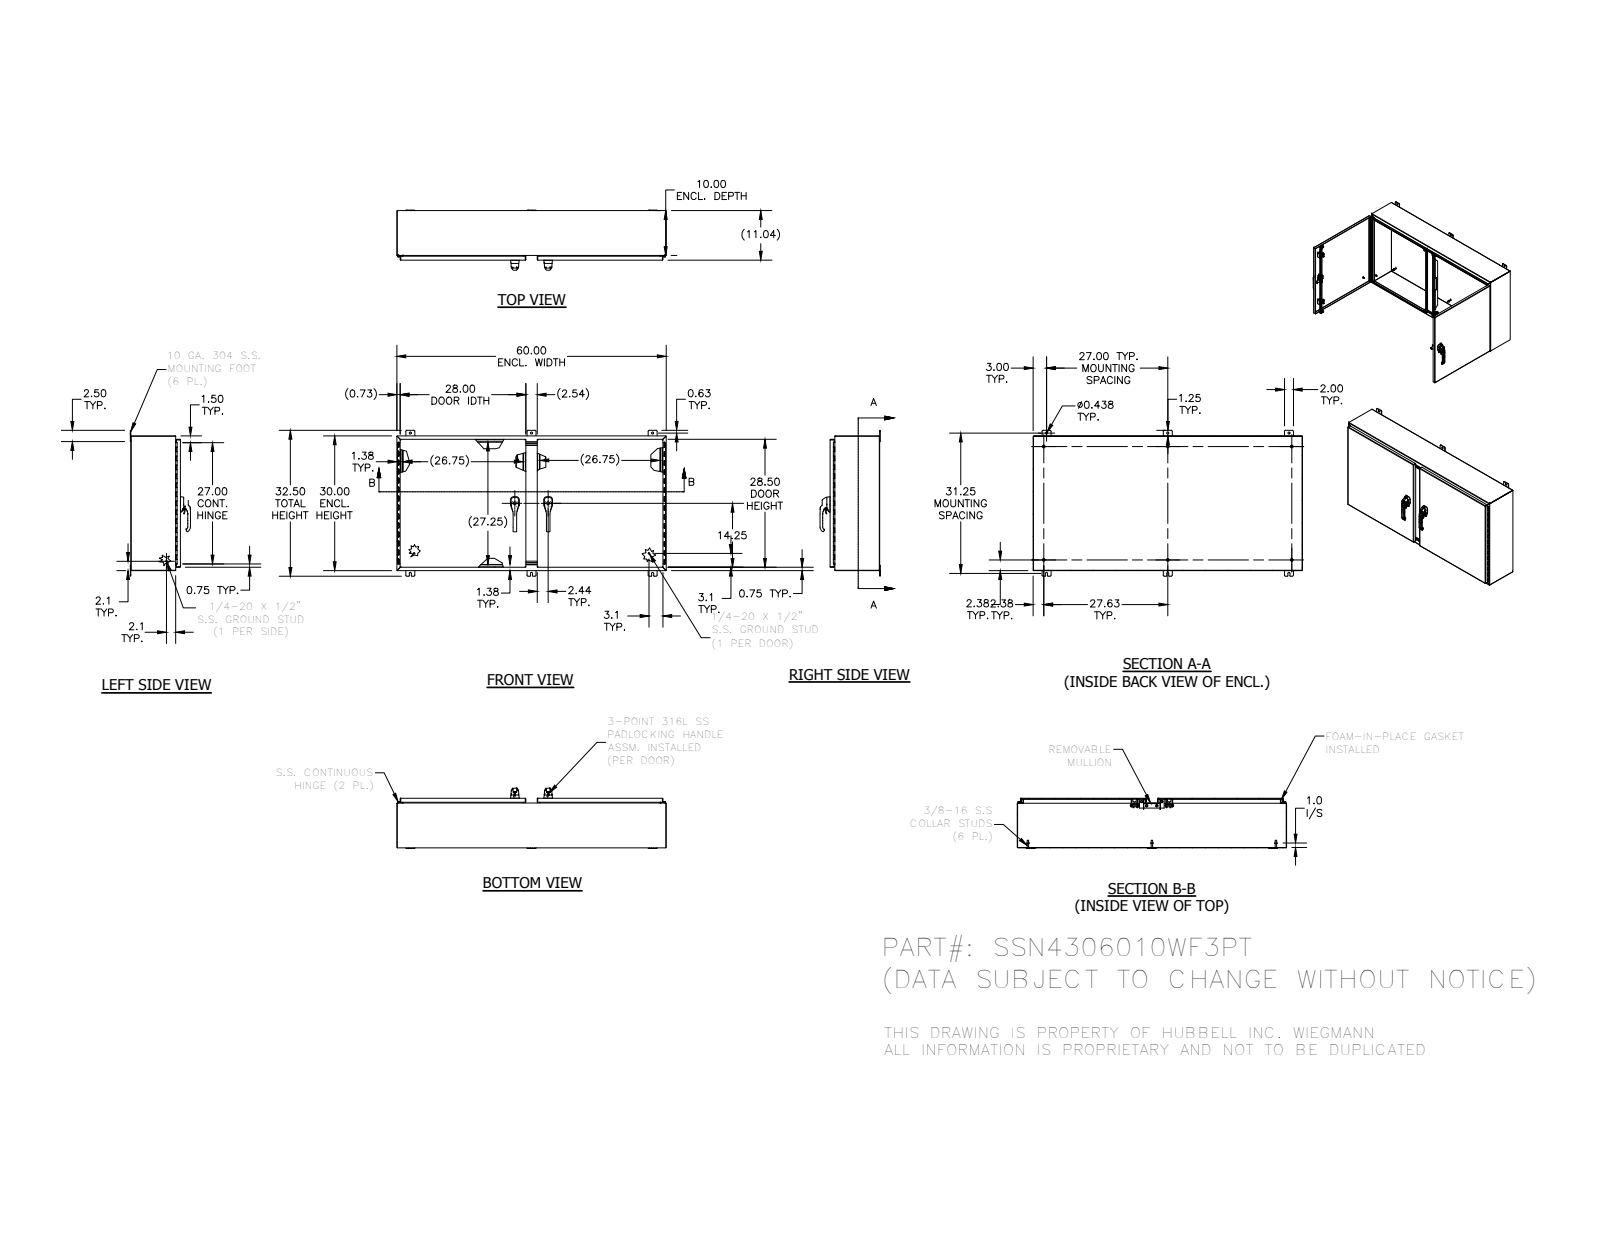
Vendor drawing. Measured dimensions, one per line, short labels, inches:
name: SSN43010WF3PTLRS; SSN43060WF3PTLDR; 1091-BR11_AF0; 1091-74-03 (+8 more)
written by: SolidWorks 2014 (AUTOMOTIVE_DESIGN)
unit: in
bodies: 125 solids, 6482 faces (2308 planar, 2658 cylindrical, 1516 other)
size: 60 × 32.5 × 13.409
volume: 530.8 in³; area: 13 045 in²
holes: 12× ⌀0.262, 8× ⌀0.187, 6× ⌀0.213, 6× ⌀0.28, 6× ⌀0.438, 4× ⌀0.196, 4× ⌀0.252, 4× ⌀0.281, 4× ⌀0.315, 4× ⌀0.4, 4× ⌀0.402, 4× ⌀0.45
bosses: 9× ⌀0.25, 6× ⌀0.625, 6× ⌀0.533, 6× ⌀0.33, 5× ⌀0.236, 4× ⌀0.531, 4× ⌀0.438, 4× ⌀0.435
rounds: 317× R0.02, 221× R0.012, 39× R0.019, 33× R0.031, 31× R0.125, 30× R0.05, 30× R0.25, 25× R0.079
face distances: 0.074, 0.094, 10.942, 10.868, 11.035, 10.961, 29.926, 9.926, 29.852, 59.926
hole spacings: 0.38, 0.76, 7.417, 0.492, 0.492, 0.886, 1.236, 1.376
